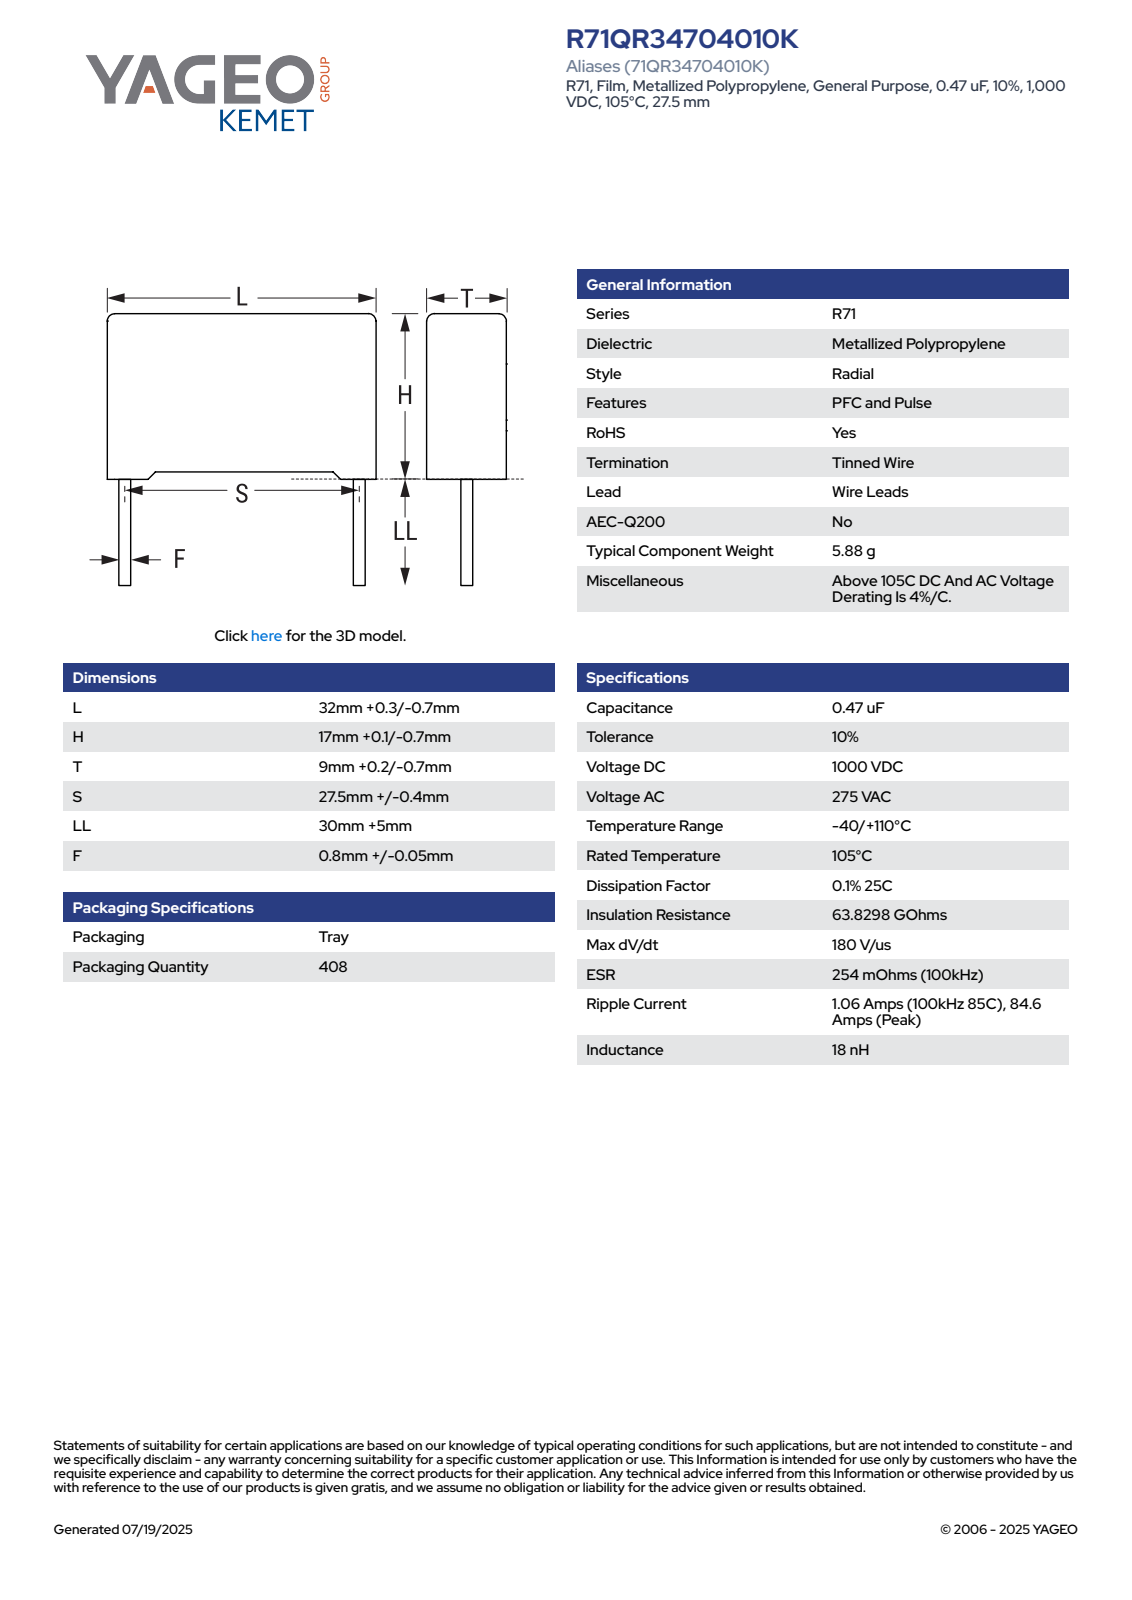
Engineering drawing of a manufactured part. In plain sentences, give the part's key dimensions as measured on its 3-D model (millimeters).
The part is named "CFR_RB2_32X17X9_L32.3H17.1T9.2S27.5LL35F0.85". Its 3-D file was written by "SolidWorks 2021 (AUTOMOTIVE_DESIGN)". It is 4 solids with 85 faces: 77 planar, 8 cylindrical and 0 other. Overall it measures 52.1 by 32.3 by 9.21 millimeters. Its volume is 4 929 cubic millimeters and its surface area 2 266 square millimeters. Round bosses or shafts: 2 of diameter 0.85. Partial cylindrical surfaces (rounded edges, fillets, slot ends): 4 of radius 0.5. The main face-to-face distances are 9.2, 16.35, 32.3, 16.51, 0.59, 0.75, 17.1, 1.08, 9.21, 8.12.
